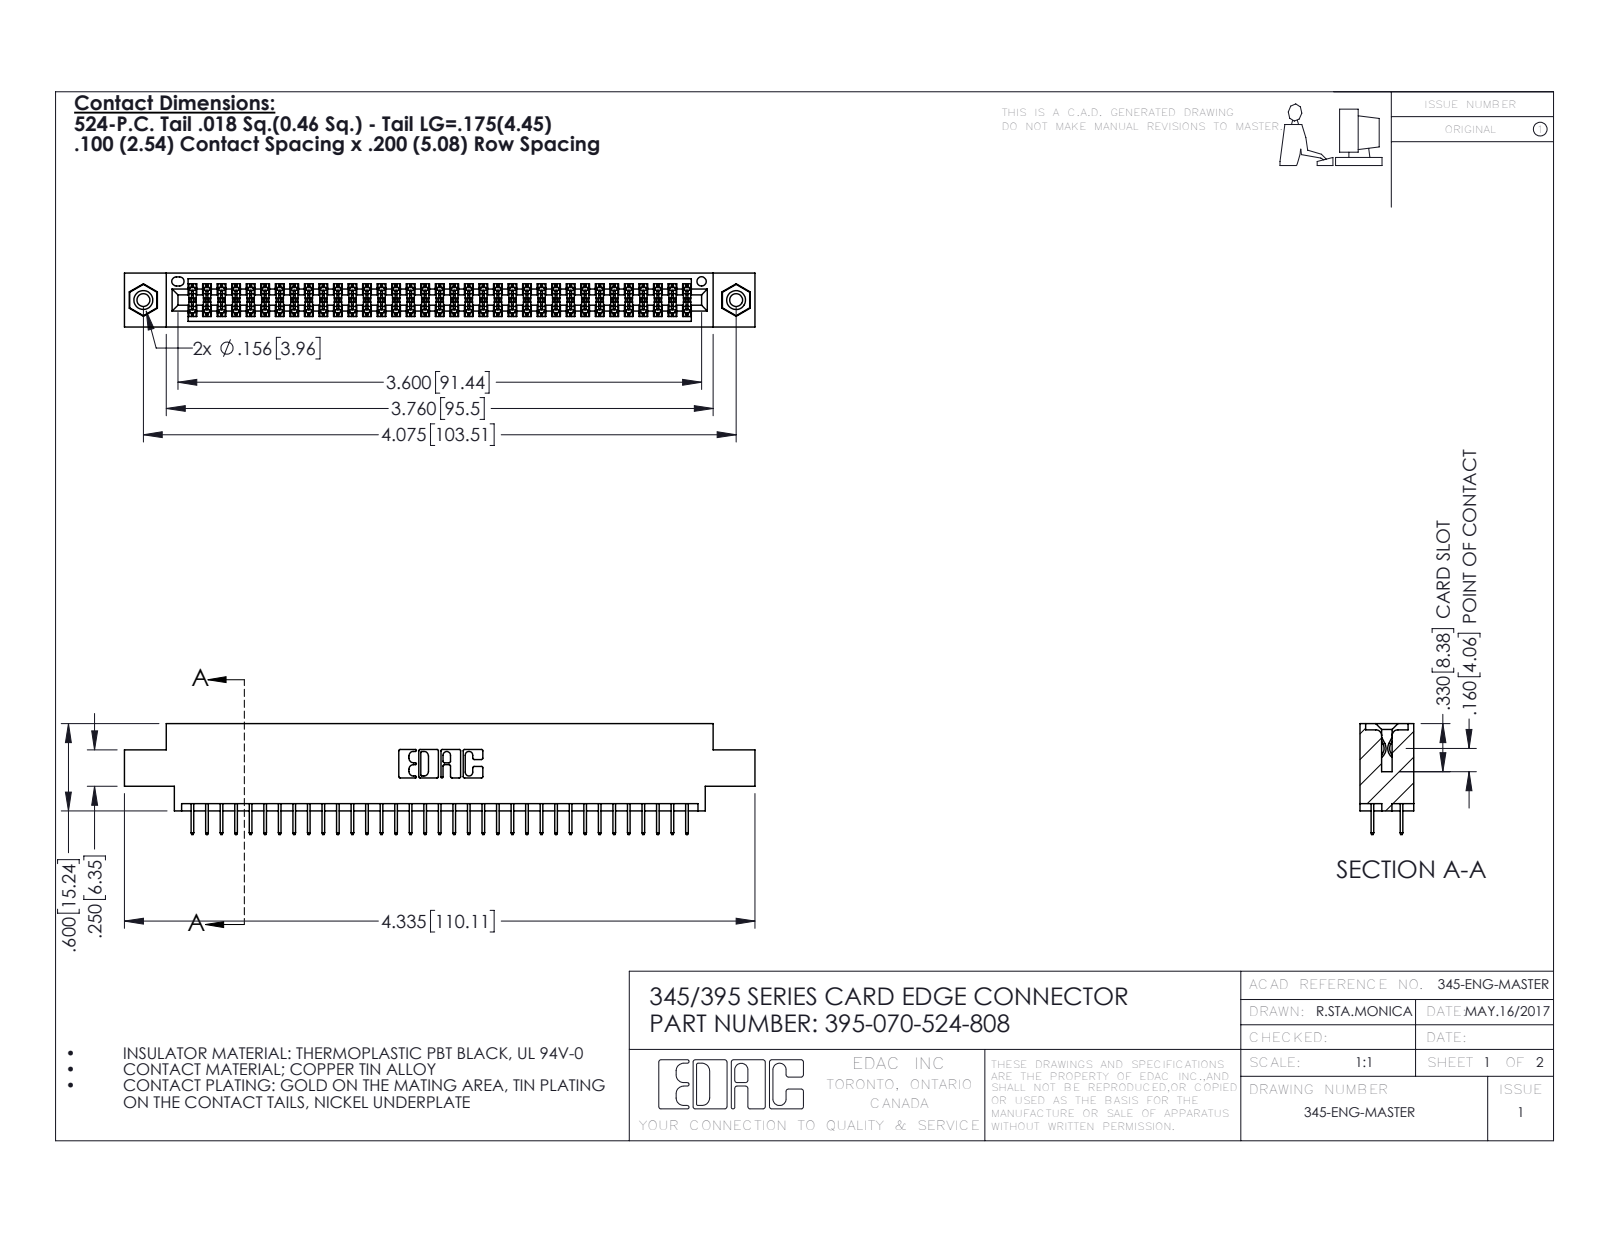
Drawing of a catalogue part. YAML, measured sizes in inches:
part_name: "345-250-001_345-250-003-102; 395-070-524-808; 345 Part_0.170 Offset - 0.156 Dia-TI; 345-292-001_345-293-124"
step_written_by: "SolidWorks 2016 (CONFIG_CONTROL_DESIGN)"
units: inches
bodies: {solids: 73, faces: 3970, planar: 2846, cylindrical: 1108, other: 16}
overall_size: [4.335, 0.762, 0.37]
volume: 0.635
surface_area: 23.44
round_holes:
  - {diameter: 0.089, count: 2}
  - {diameter: 0.125, count: 2}
  - {diameter: 0.156, count: 2}
  - {diameter: 0.064, count: 1}
round_bosses_or_shafts:
  - {diameter: 0.155, count: 2}
partial_cylinders:
  - {radius: 0.006, count: 105}
  - {radius: 0.01, count: 22}
  - {radius: 0.007, count: 6}
  - {radius: 0.031, count: 6}
  - {radius: 0.026, count: 3}
  - {radius: 0.014, count: 2}
  - {radius: 0.019, count: 2}
  - {radius: 0.022, count: 2}
face_to_face_distances: [0.072, 0.298, 0.37, 0.2, 0.098, 0.272, 0.025, 0.225, 0.175, 0.072]
hole_center_spacings: [0.27, 3.839, 4.075]
